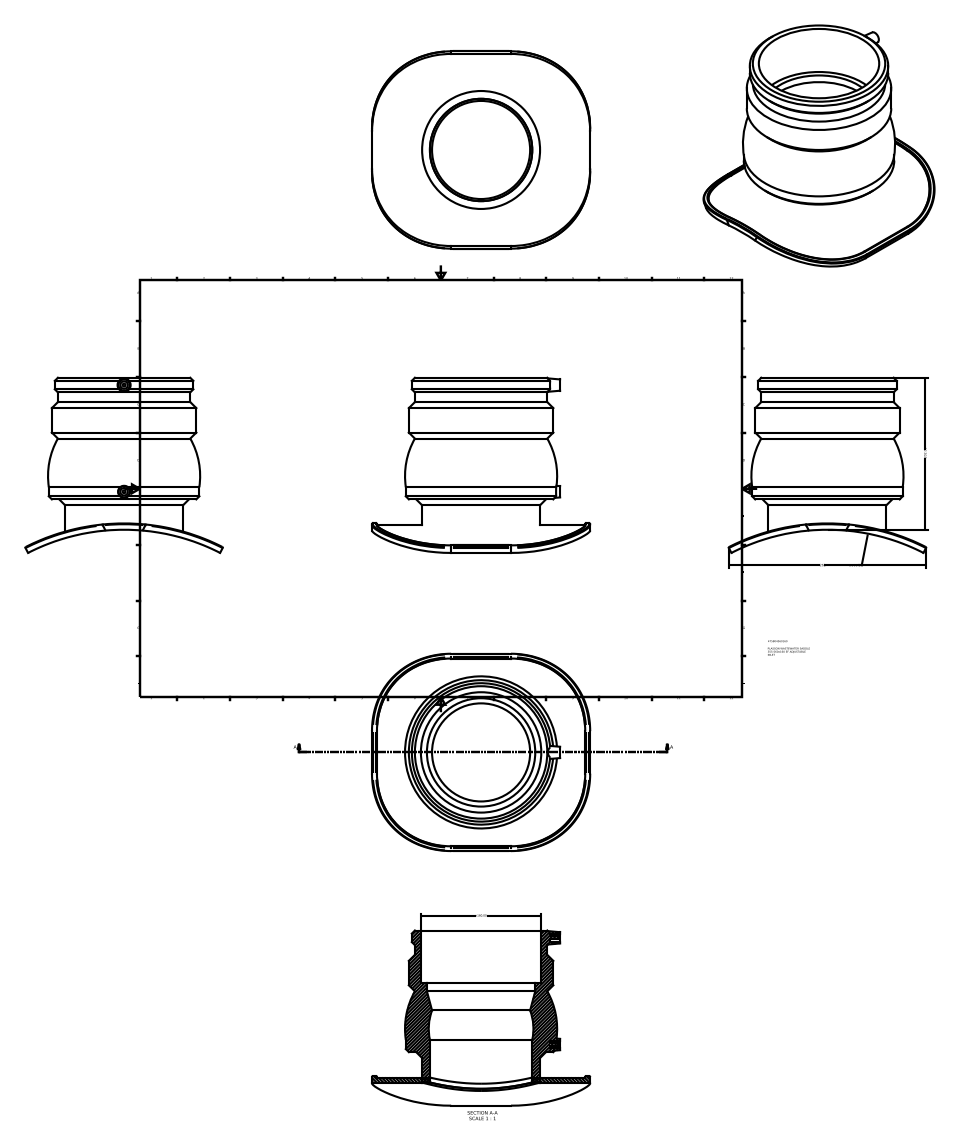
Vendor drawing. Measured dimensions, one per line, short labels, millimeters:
name: 475804560160
written by: Autodesk Inventor 2015 (AUTOMOTIVE_DESIGN)
unit: mm
bodies: 2 solids, 69 faces (17 planar, 29 cylindrical, 23 other)
size: 290 × 262.27 × 232.8
volume: 2 458 000 mm³; area: 363 393 mm²
holes: 2× ⌀10, 1× ⌀136, 1× ⌀144, 1× ⌀160
bosses: 2× ⌀4, 1× ⌀200, 1× ⌀192, 1× ⌀184, 1× ⌀176, 1× ⌀156.8
rounds: 4× R1.05, 4× R98.62, 4× R105.2, 1× R280, 1× R286.57, 1× R288.4
face distances: 161.6, 91.6, 70, 290, 6.57, 250, 40, 236, 14, 54
hole spacings: 141.82
